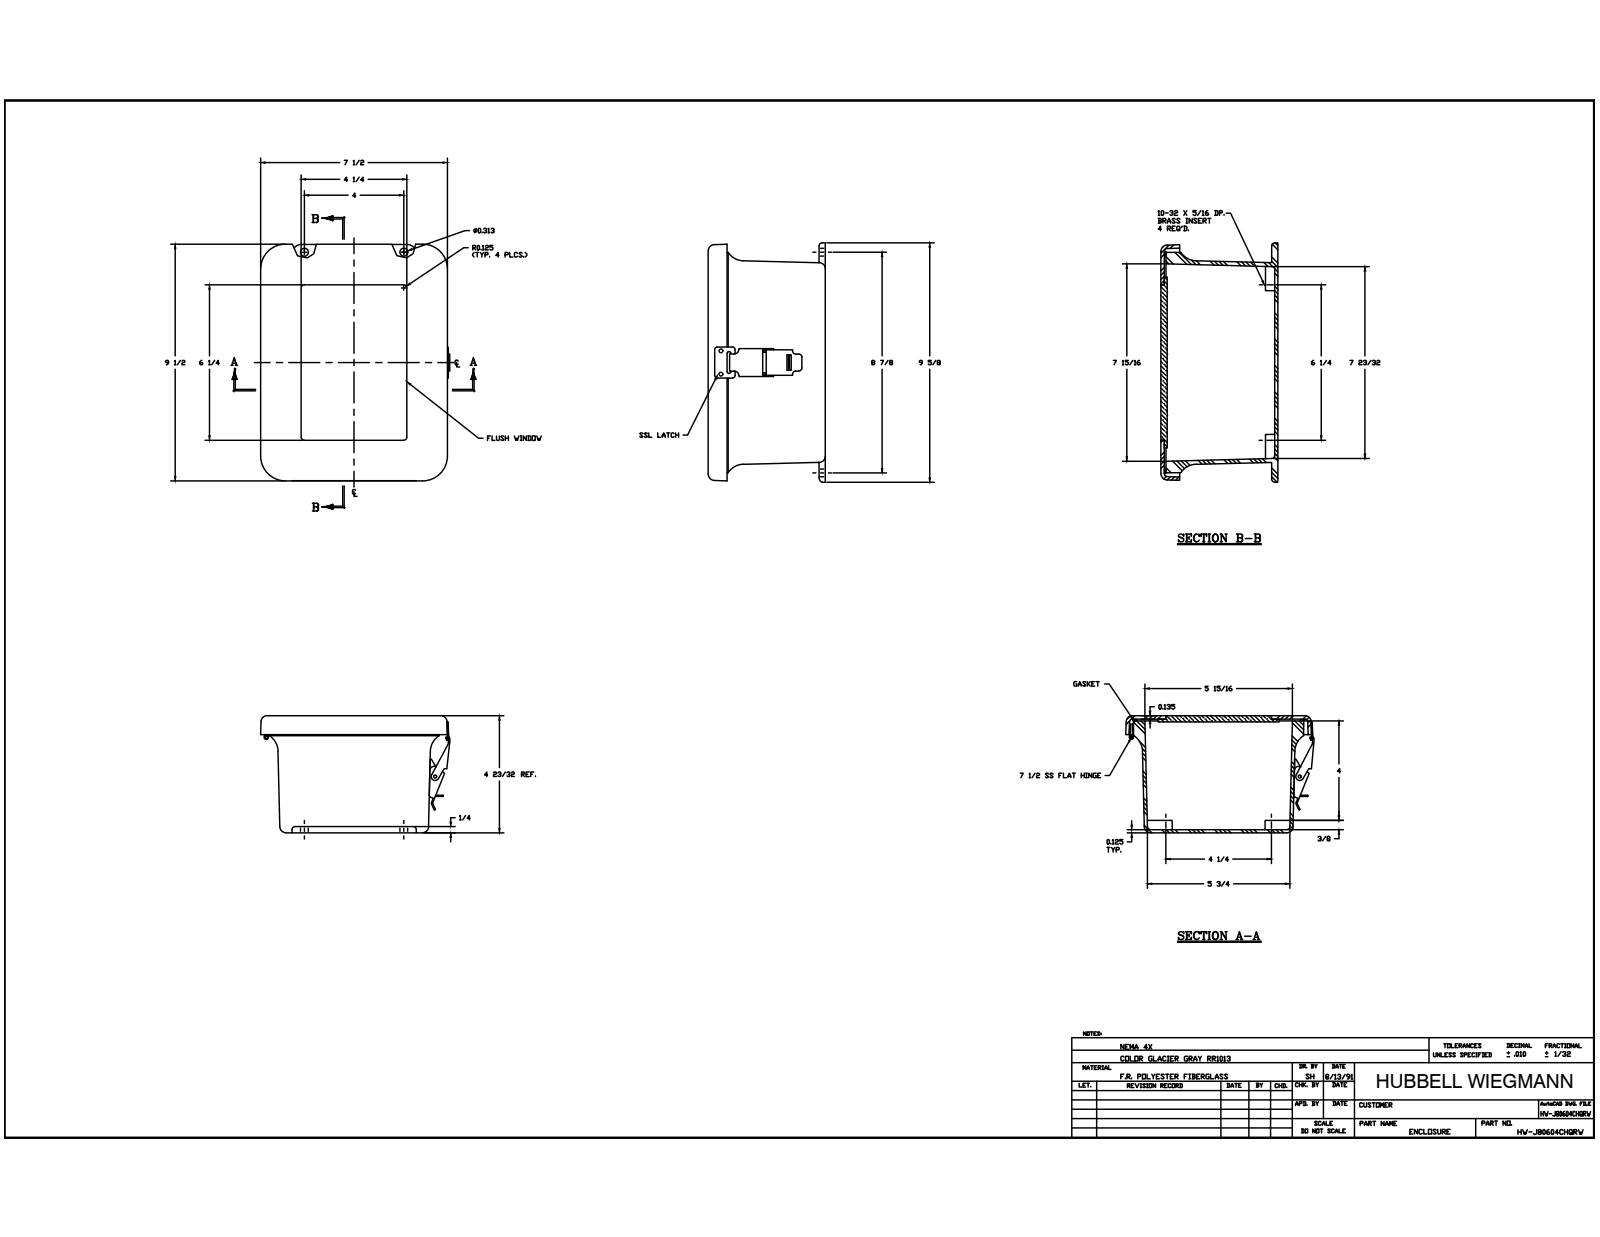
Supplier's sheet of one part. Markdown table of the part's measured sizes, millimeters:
| quantity | value |
| --- | --- |
| part name | J806HL_2; RMINS45821P_207; RMINS45821P_208; RMINS45821P_209 (+8 more) |
| STEP written by | Autodesk Inventor 2014 (AUTOMOTIVE_DESIGN) |
| units | millimeters |
| bodies | 29 solids, 715 faces (298 planar, 290 cylindrical, 127 other) |
| overall size | 244.47 × 193.61 × 119.36 |
| volume | 807 356 mm³ |
| surface area | 413 663 mm² |
| round holes (diameter × count) | 3.56 × 11, 3.33 × 6, 3.86 × 5, 2.64 × 4, 3.96 × 4, 5.54 × 4, 3.3 × 2, 3.43 × 2, 2.16 × 1, 9.52 × 1 |
| round bosses / shafts (diameter × count) | 3.17 × 12, 6.35 × 8, 6.86 × 4, 7.62 × 1, 4.31 × 1, 3.94 × 1, 3.05 × 1 |
| partial cylindrical surfaces (radius × count) | 0.79 × 20, 3.17 × 20, 0.38 × 12, 6.35 × 12, 1.14 × 8, 0.76 × 6, 0.57 × 5, 1.52 × 4 |
| main face-to-face distances | 3.18, 3.43, 115.93, 119.36, 3.17, 6.35, 113.01, 112.75, 116.18, 109.83 |
| hole center spacings | 88.9, 33.68, 133.89, 184.12, 225.15, 6.36, 19.05, 36.93 |
